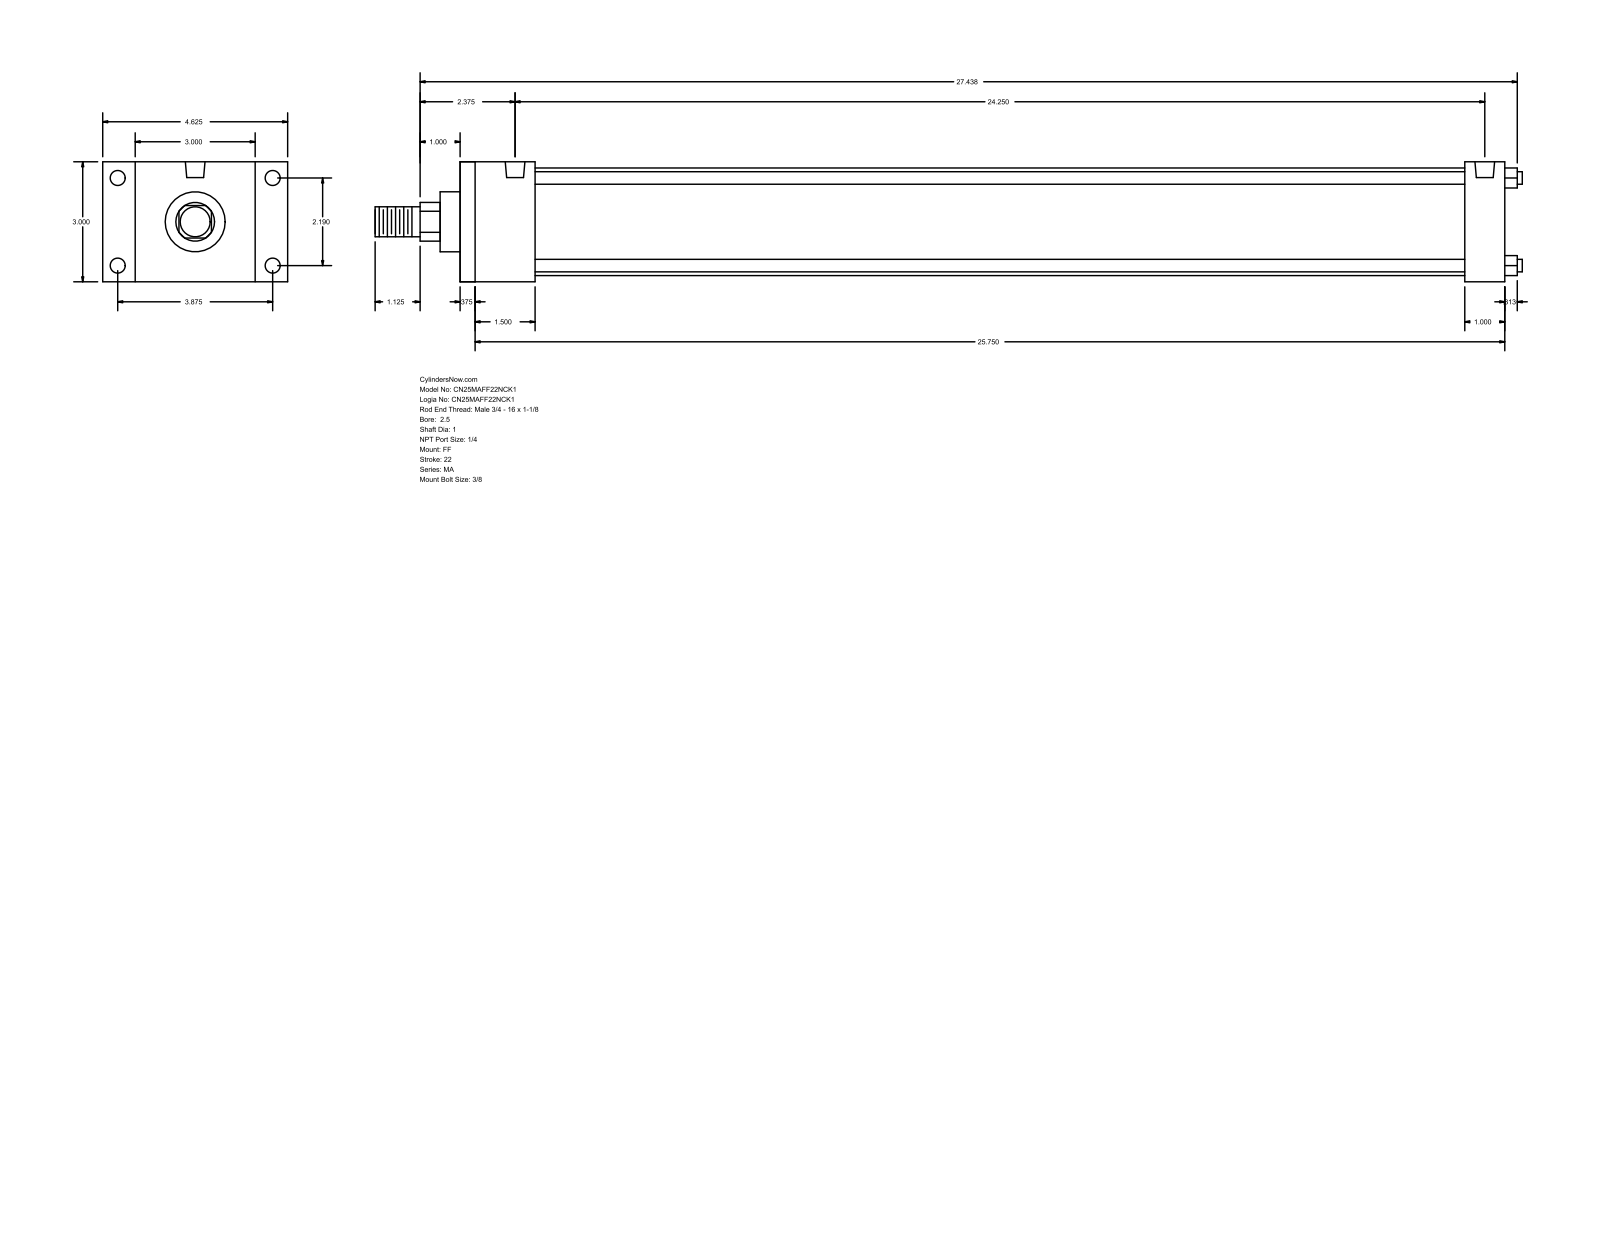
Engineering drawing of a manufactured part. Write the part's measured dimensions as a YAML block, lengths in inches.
part_name: "MA_FF__0250_1"
step_written_by: "GSSL Pune (CONFIG_CONTROL_DESIGN)"
units: inches
bodies: {solids: 0, faces: 92, planar: 64, cylindrical: 28, other: 0}
overall_size: [28.687, 4.625, 3]
round_holes:
  - {diameter: 0.313, count: 4}
  - {diameter: 0.375, count: 4}
  - {diameter: 0.492, count: 2}
round_bosses_or_shafts:
  - {diameter: 0.313, count: 4}
  - {diameter: 2.69, count: 1}
  - {diameter: 1.5, count: 1}
  - {diameter: 1, count: 1}
  - {diameter: 0.75, count: 1}
partial_cylinders:
  - {radius: 0.484, count: 1}
face_to_face_distances: [3, 26.125, 0.375, 25.75, 1, 1.875, 25.125, 1.5, 24.75, 23.25]
hole_center_spacings: [2.19, 3.875, 4.451, 24.25]
